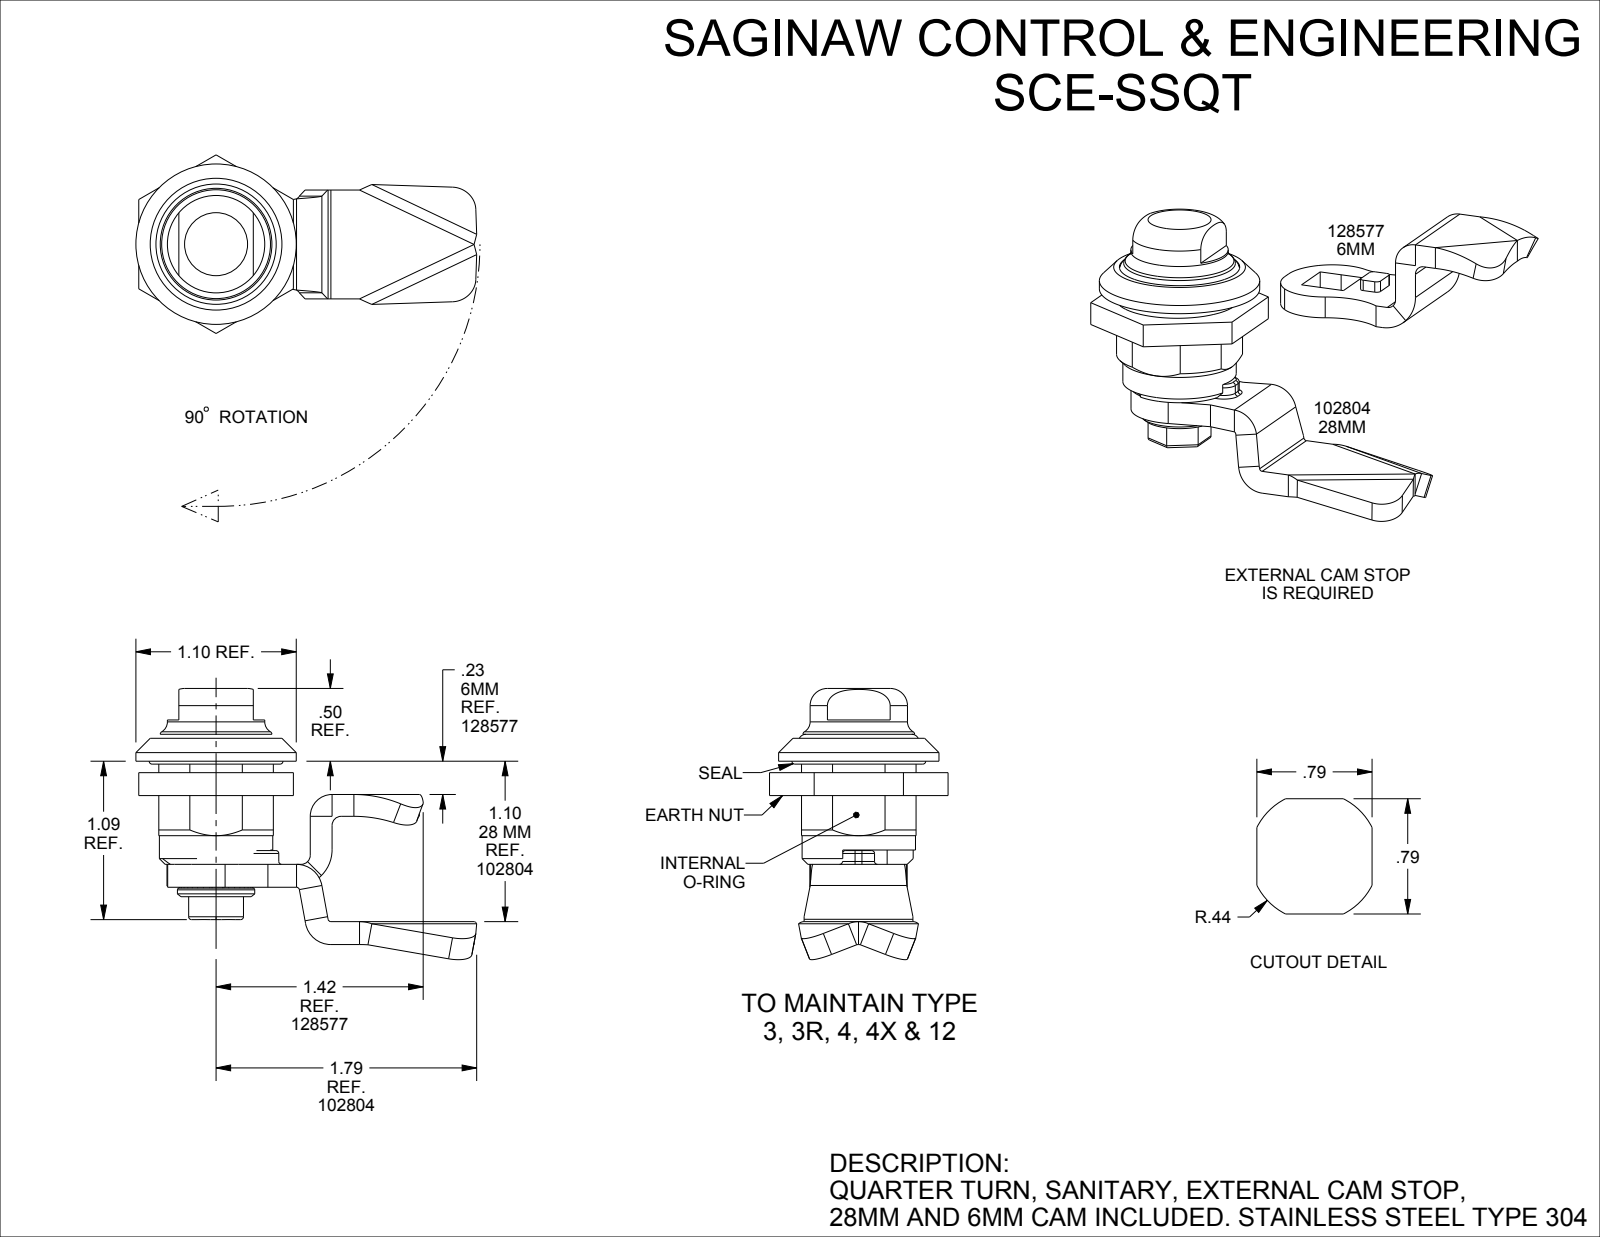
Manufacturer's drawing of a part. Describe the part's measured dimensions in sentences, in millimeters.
The part is named "SCE-SSQT". Its 3-D file was written by "SolidWorks 2021 (AUTOMOTIVE_DESIGN)". It is 12 solids with 275 faces: 124 planar, 85 cylindrical and 66 other. Overall it measures 91.3 by 59.5 by 47.3 millimeters. Its volume is 18 910 cubic millimeters and its surface area 14 130 square millimeters. Round holes: 1 of diameter 5, 1 of diameter 10, 1 of diameter 16.1, 1 of diameter 20.2, 1 of diameter 21, 1 of diameter 27. Round bosses or shafts: 1 of diameter 28, 1 of diameter 23, 1 of diameter 19.8, 1 of diameter 17, 1 of diameter 16, 1 of diameter 13.5, 1 of diameter 12.5, 1 of diameter 9.9. Partial cylindrical surfaces (rounded edges, fillets, slot ends): 16 of radius 0.5, 4 of radius 0.8, 4 of radius 4.5, 4 of radius 7.6, 2 of radius 2.2, 2 of radius 4, 2 of radius 8.7, 2 of radius 10.2. The main face-to-face distances are 4, 16, 6, 3.8, 26, 10, 20, 22, 14, 12.2.
